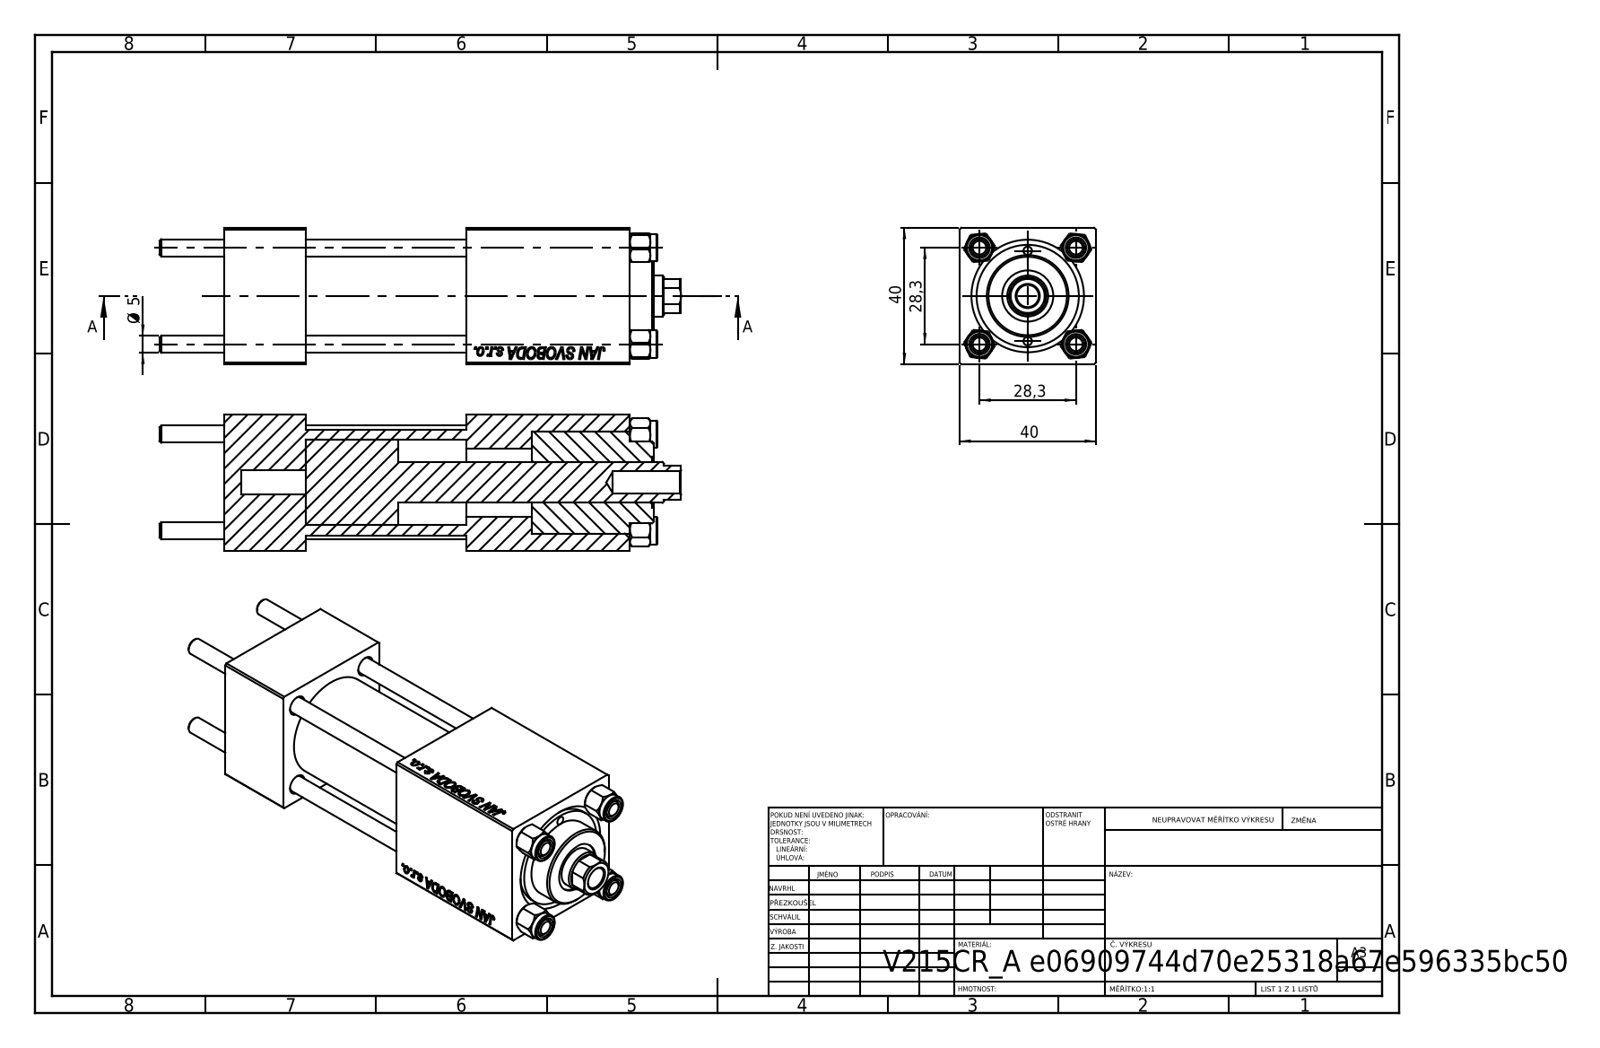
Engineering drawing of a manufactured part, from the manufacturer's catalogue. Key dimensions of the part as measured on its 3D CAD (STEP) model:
Part name (STEP PRODUCT): CR025_012_A_0_G_A_G_M_020_+#_##_TYCINKA; NUT_M5; V215CR_VCP; V215CR_BODY_A (+1 more)
STEP written by: SolidWorks 2019 (CONFIG_CONTROL_DESIGN)
Units: millimetres
Bodies: 11 solids, 1137 faces (519 planar, 82 cylindrical, 536 other)
Overall size (bounding box): 153 × 40 × 40
Volume: 144 775 mm³ · Surface area: 58 950 mm²
Round holes (diameter × count): ⌀5 ×4, ⌀20 ×3, ⌀2.5 ×2, ⌀7 ×2, ⌀13.16 ×2, ⌀6.5 ×1, ⌀12 ×1, ⌀15 ×1, ⌀25 ×1, ⌀30 ×1
Round bosses / shafts (diameter × count): ⌀8 ×4, ⌀31 ×1, ⌀24 ×1
Partial cylindrical surfaces — rounded edges, fillets, slot ends (radius × count): R5.5 ×1
Main face-to-face distances: 40, 24, 90.3, 66.3, 119, 95, 28.7, 71, 47, 19.3
Hole centre spacings: 14.18, 20.01, 28.3, 30.84, 13.25, 40.02, 26.5, 72
